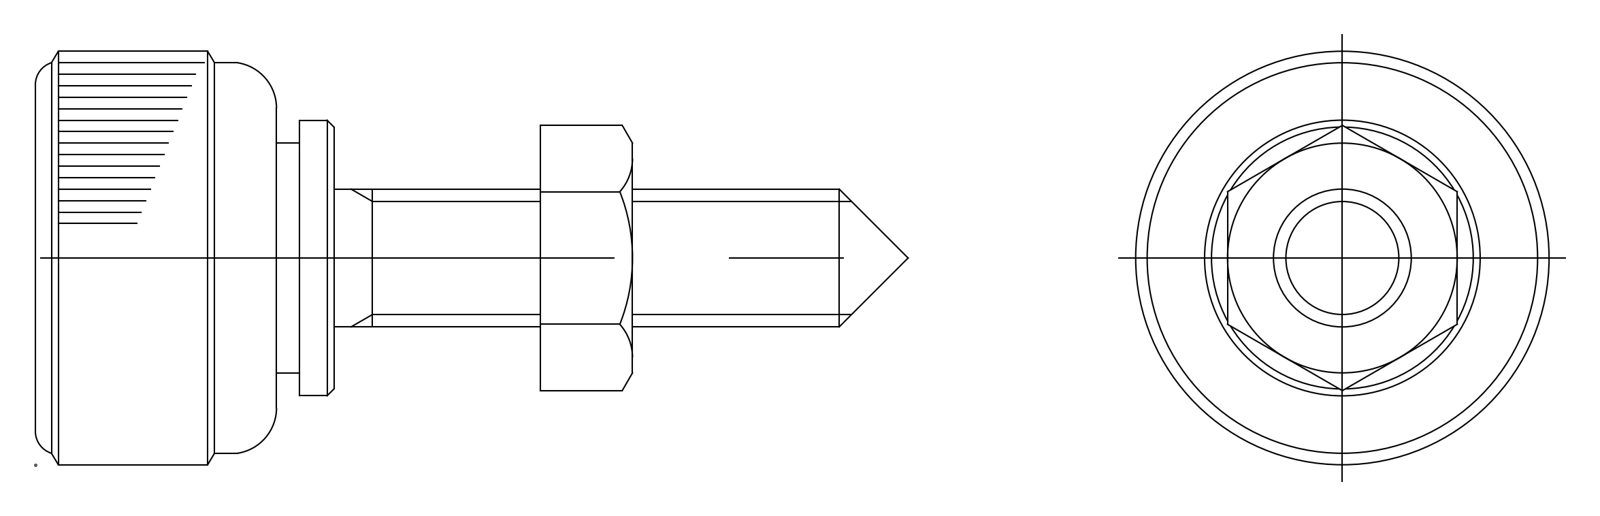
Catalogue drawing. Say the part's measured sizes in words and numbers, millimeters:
The part is named "THA_340SUS_18_6_Nツマミ; M6ナット". Its 3-D file was written by "spGate 20.6.3 (****-****-****-****) (AUTOMOTIVE_DESIGN)". It is 2 solids with 42 faces: 12 planar, 12 cylindrical and 18 other. Overall it measures 38 by 18 by 18 millimeters. Its volume is 3 708 cubic millimeters and its surface area 1 957 square millimeters. Round holes: 1 of diameter 6. Round bosses or shafts: 1 of diameter 18, 1 of diameter 17, 1 of diameter 12, 1 of diameter 10. The main face-to-face distances are 10, 13, 6.46, 19.46, 8.96, 2.5, 10.5, 5, 11.46, 13.96.
